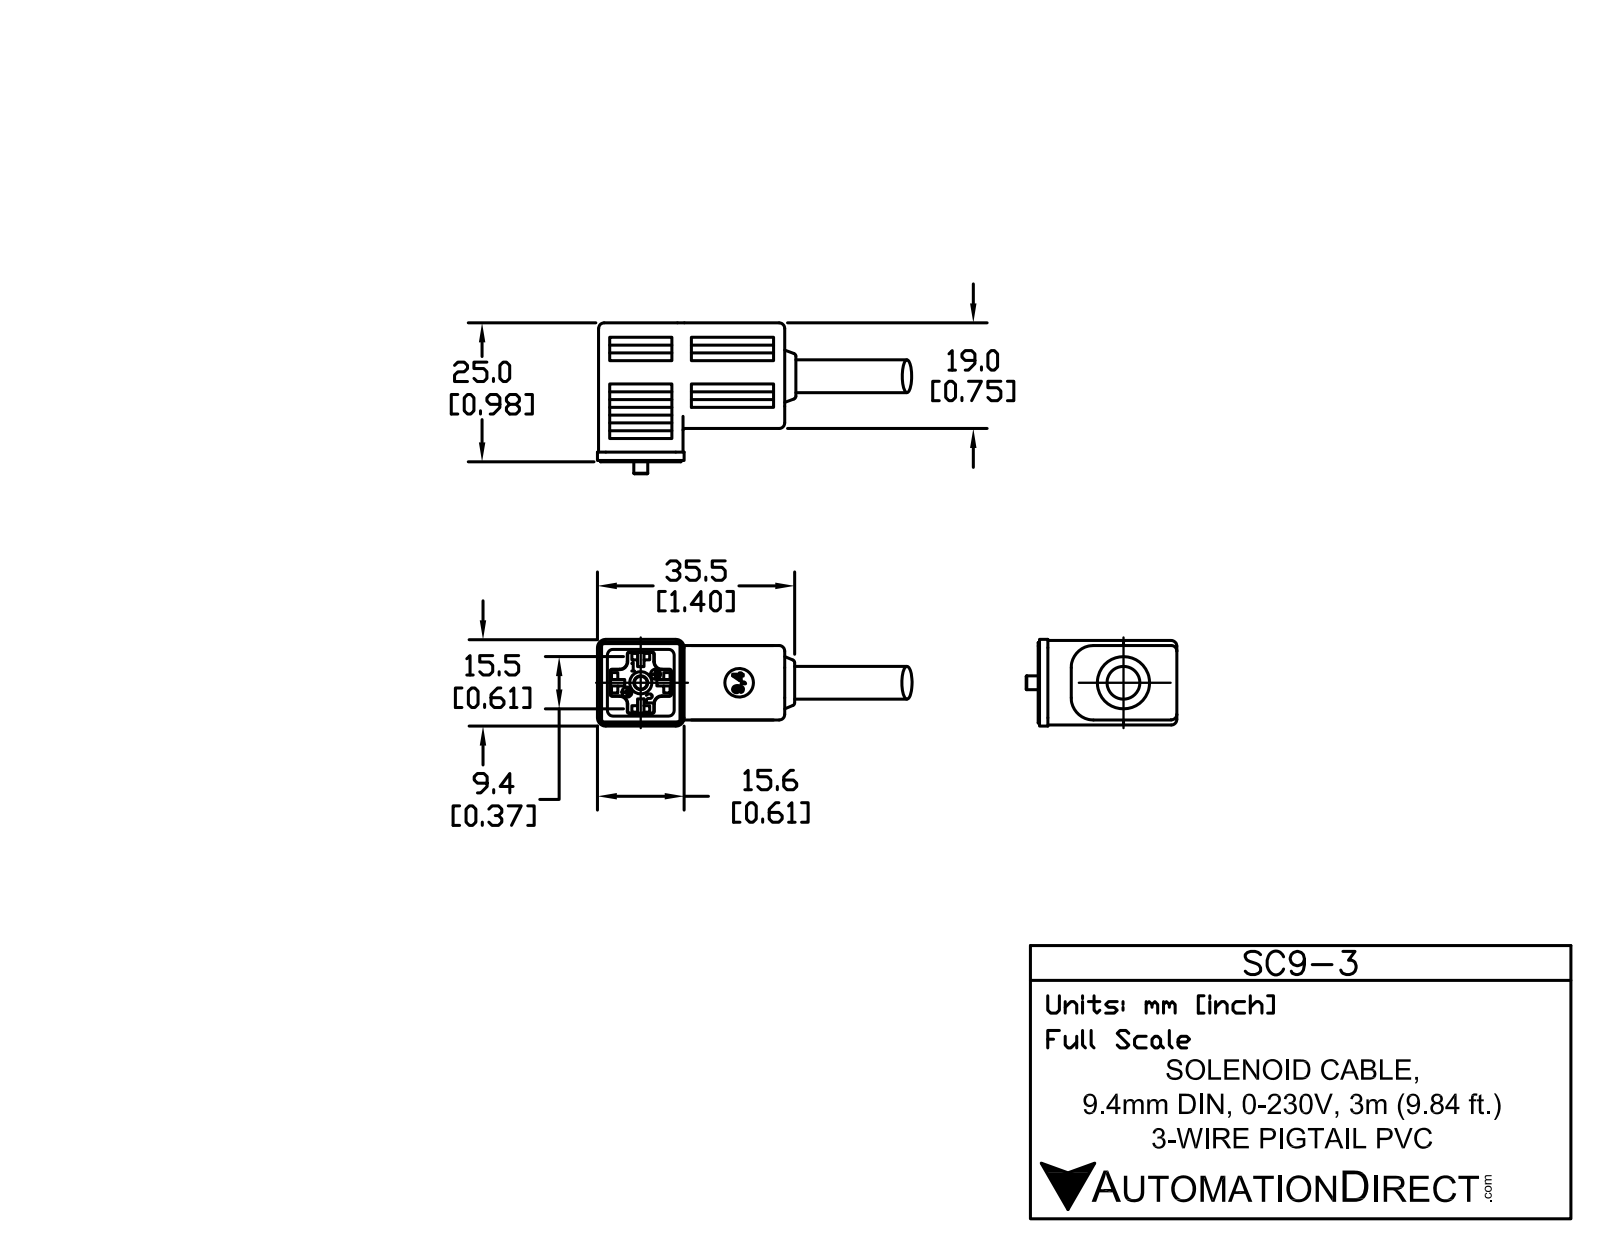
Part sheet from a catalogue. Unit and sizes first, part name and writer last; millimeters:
Units: millimetres
Overall size (bounding box): 63.37 × 33.61 × 15.77
Round holes (diameter × count): ⌀2.25 ×2, ⌀6 ×2, ⌀4 ×1
Round bosses / shafts (diameter × count): ⌀5.75 ×1, ⌀2.75 ×1
Partial cylindrical surfaces — rounded edges, fillets, slot ends (radius × count): R0.5 ×10, R0.75 ×4, R2 ×4, R0.25 ×3, R4 ×2
Main face-to-face distances: 22.24, 0.88, 1, 15.5, 23.24, 14.32, 13.75, 0.87, 14.62, 14.63
Hole centre spacings: 3.29, 3.58, 6.5
Volume: 11 179 mm³ · Surface area: 5 685 mm²
Bodies: 4 solids, 323 faces (256 planar, 36 cylindrical, 31 other)
Part name (STEP PRODUCT): SC9-3
STEP written by: SolidWorks 2011 (AUTOMOTIVE_DESIGN)
